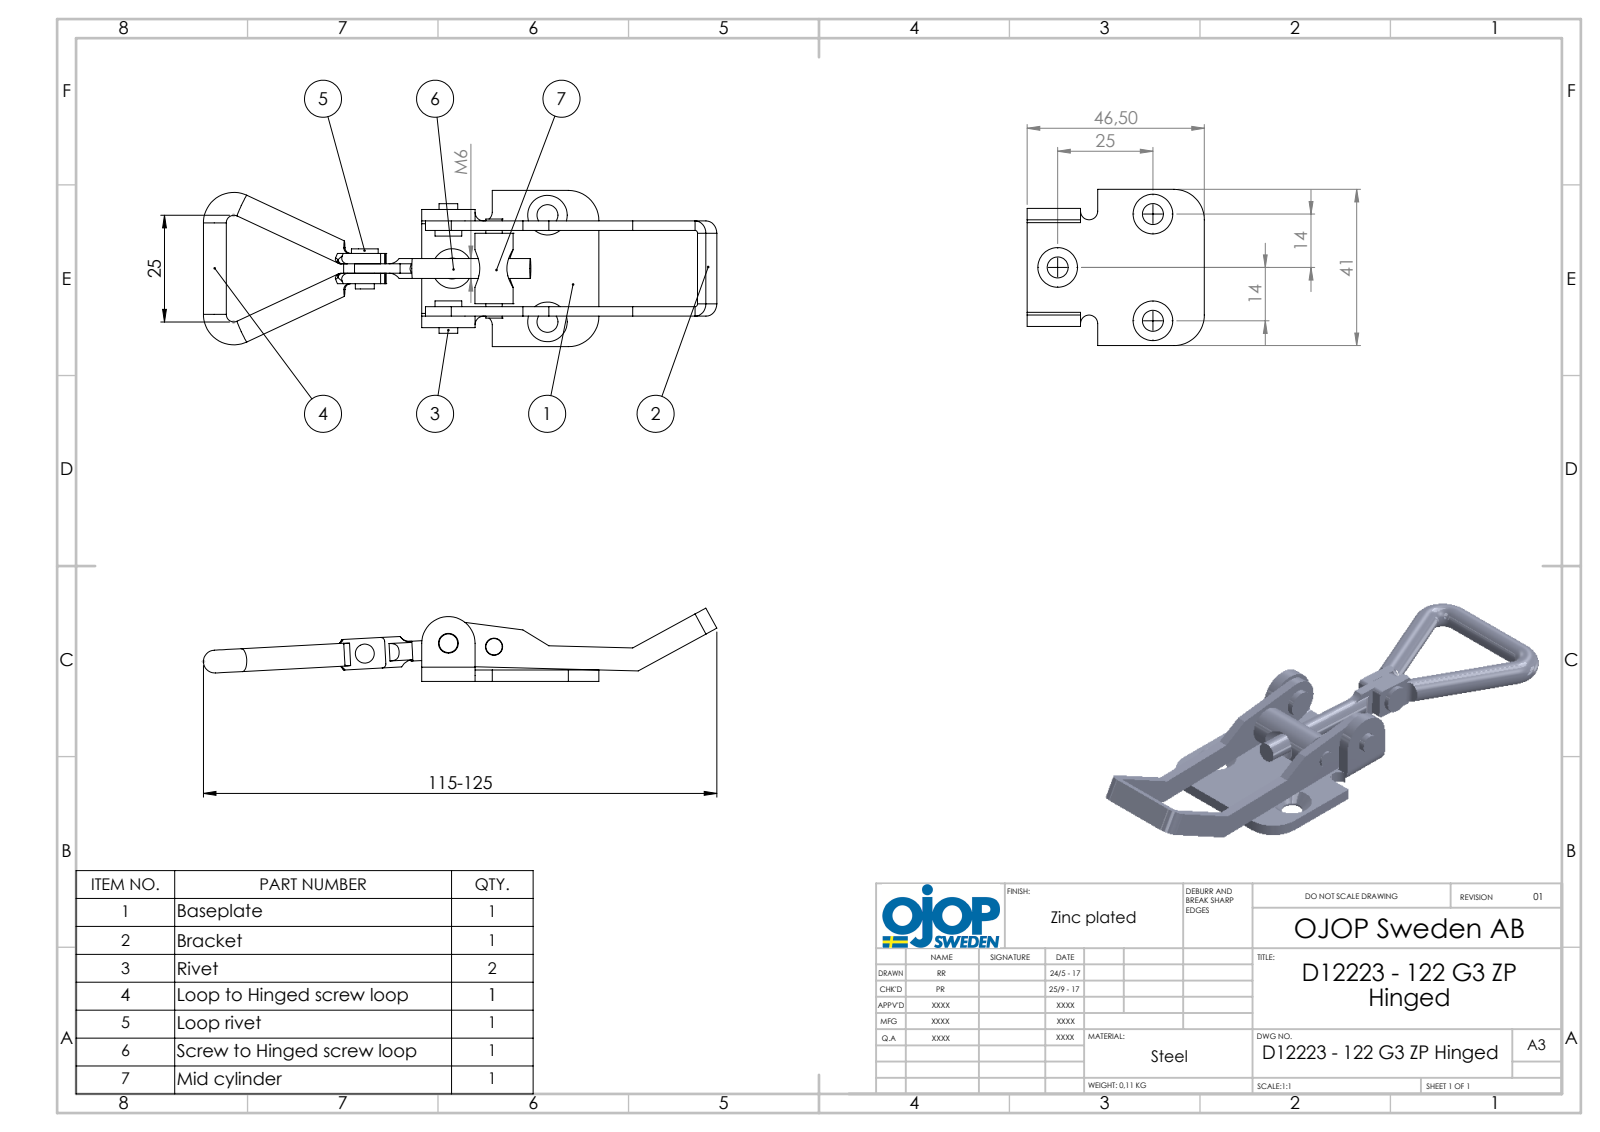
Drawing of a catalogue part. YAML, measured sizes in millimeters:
part_name: "platta; D12223 - 122 G3 ZP Hinged; nit; bygel (+4 more)"
step_written_by: "SolidWorks 2015 (AUTOMOTIVE_DESIGN)"
units: millimeters
bodies: {solids: 8, faces: 192, planar: 78, cylindrical: 80, other: 34}
overall_size: [134.76, 41, 19.23]
volume: 14702
surface_area: 13138
round_holes:
  - {diameter: 5.2, count: 3}
  - {diameter: 5.5, count: 3}
  - {diameter: 4.5, count: 1}
  - {diameter: 5, count: 1}
round_bosses_or_shafts:
  - {diameter: 6, count: 3}
  - {diameter: 7, count: 2}
  - {diameter: 10, count: 1}
  - {diameter: 5.21, count: 1}
  - {diameter: 5.2, count: 1}
  - {diameter: 4.9, count: 1}
  - {diameter: 4.3, count: 1}
partial_cylinders:
  - {radius: 0.74, count: 4}
  - {radius: 3, count: 4}
  - {radius: 1, count: 2}
  - {radius: 1.5, count: 2}
  - {radius: 2.25, count: 2}
  - {radius: 3.24, count: 2}
  - {radius: 3.74, count: 2}
  - {radius: 8, count: 2}
face_to_face_distances: [3, 2.5, 22.5, 25, 20, 6, 28, 25.5, 5.5, 11.22]
hole_center_spacings: [28.65, 12.01, 22.12, 28, 33.98]
